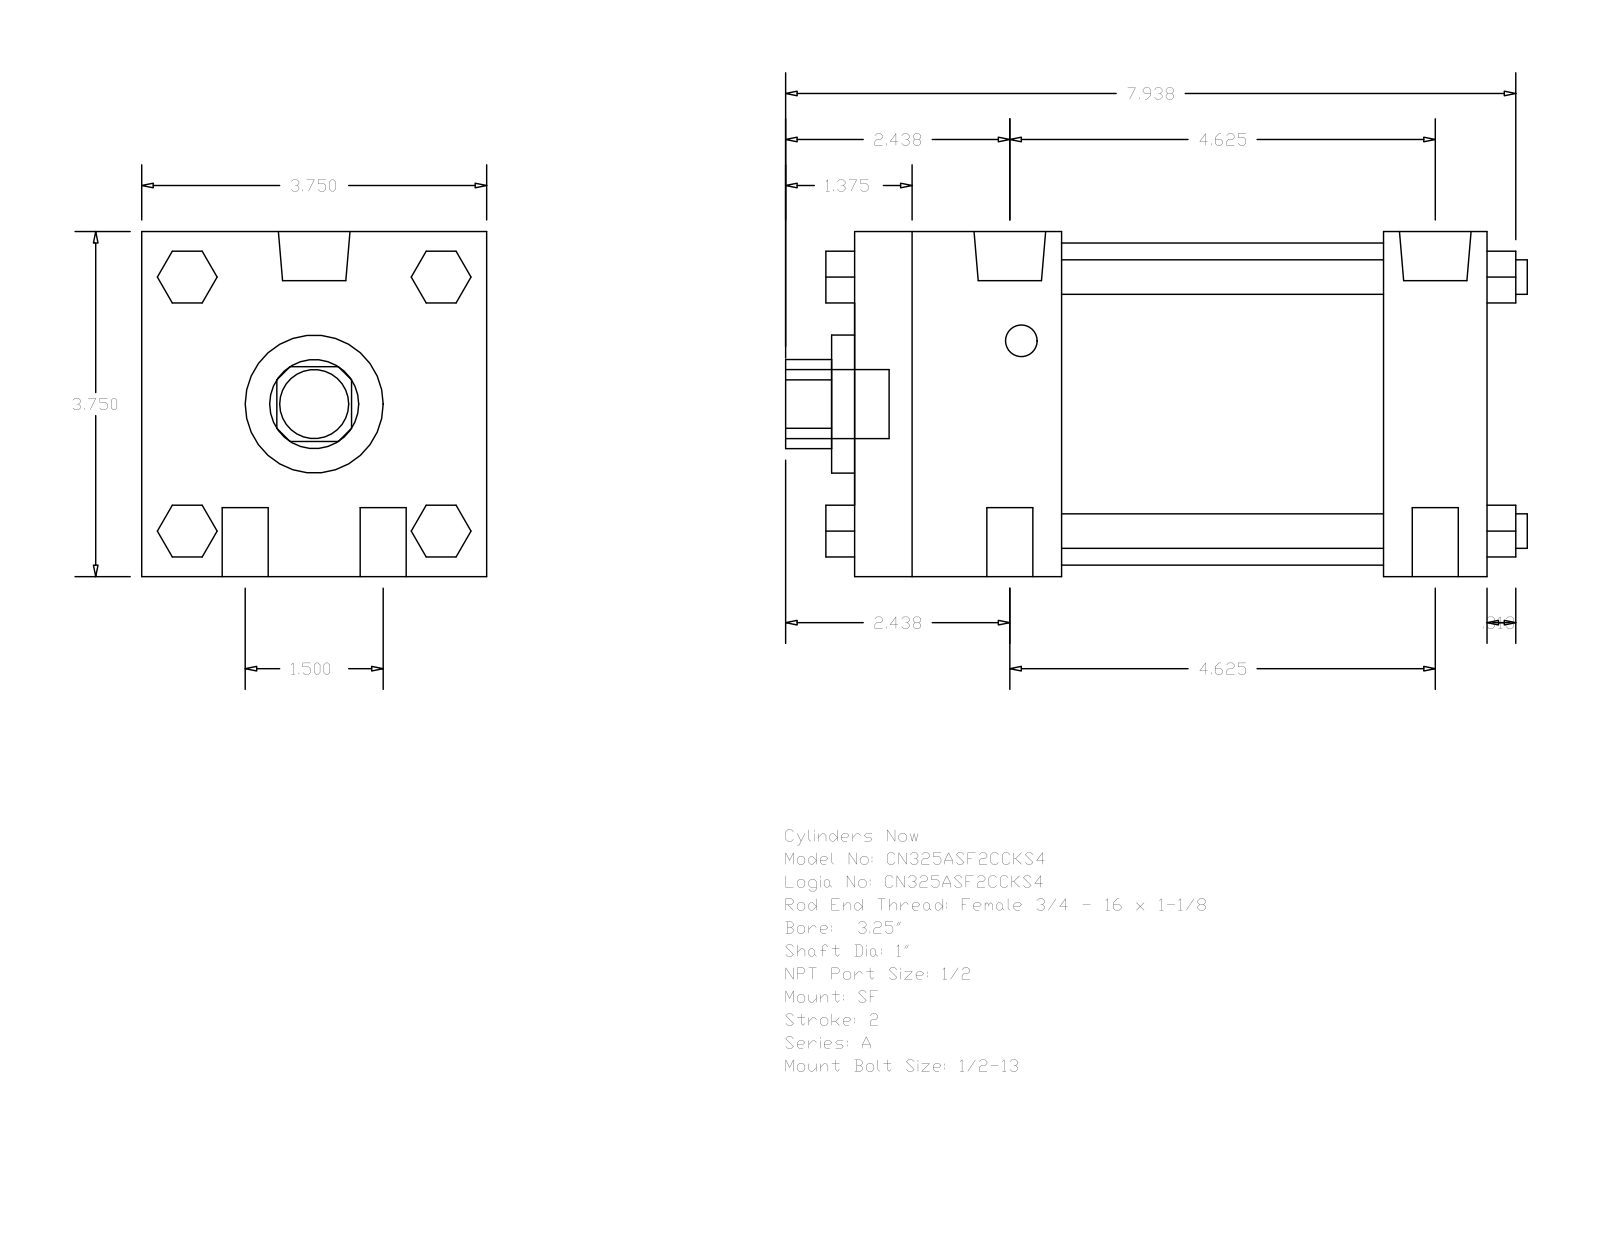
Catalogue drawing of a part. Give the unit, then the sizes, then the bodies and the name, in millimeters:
Units: millimetres
Overall size (bounding box): 204.79 × 95.25 × 95.25
Round holes (diameter × count): ⌀25.4 ×1, ⌀38.1 ×1, ⌀88.9 ×1
Round bosses / shafts (diameter × count): ⌀12.7 ×4, ⌀9.53 ×4, ⌀19.77 ×2, ⌀8.73 ×2, ⌀19.05 ×1
Partial cylindrical surfaces — rounded edges, fillets, slot ends (radius × count): R12.29 ×1
Main face-to-face distances: 95.24, 174.63, 146.05, 28.58, 57.15, 88.9, 117.48, 14.28, 35.05, 60.71
Bodies: 0 solids, 124 faces (94 planar, 30 cylindrical, 0 other)
Part name (STEP PRODUCT): A_SF__0325_1
STEP written by: GSSL Pune (CONFIG_CONTROL_DESIGN)
